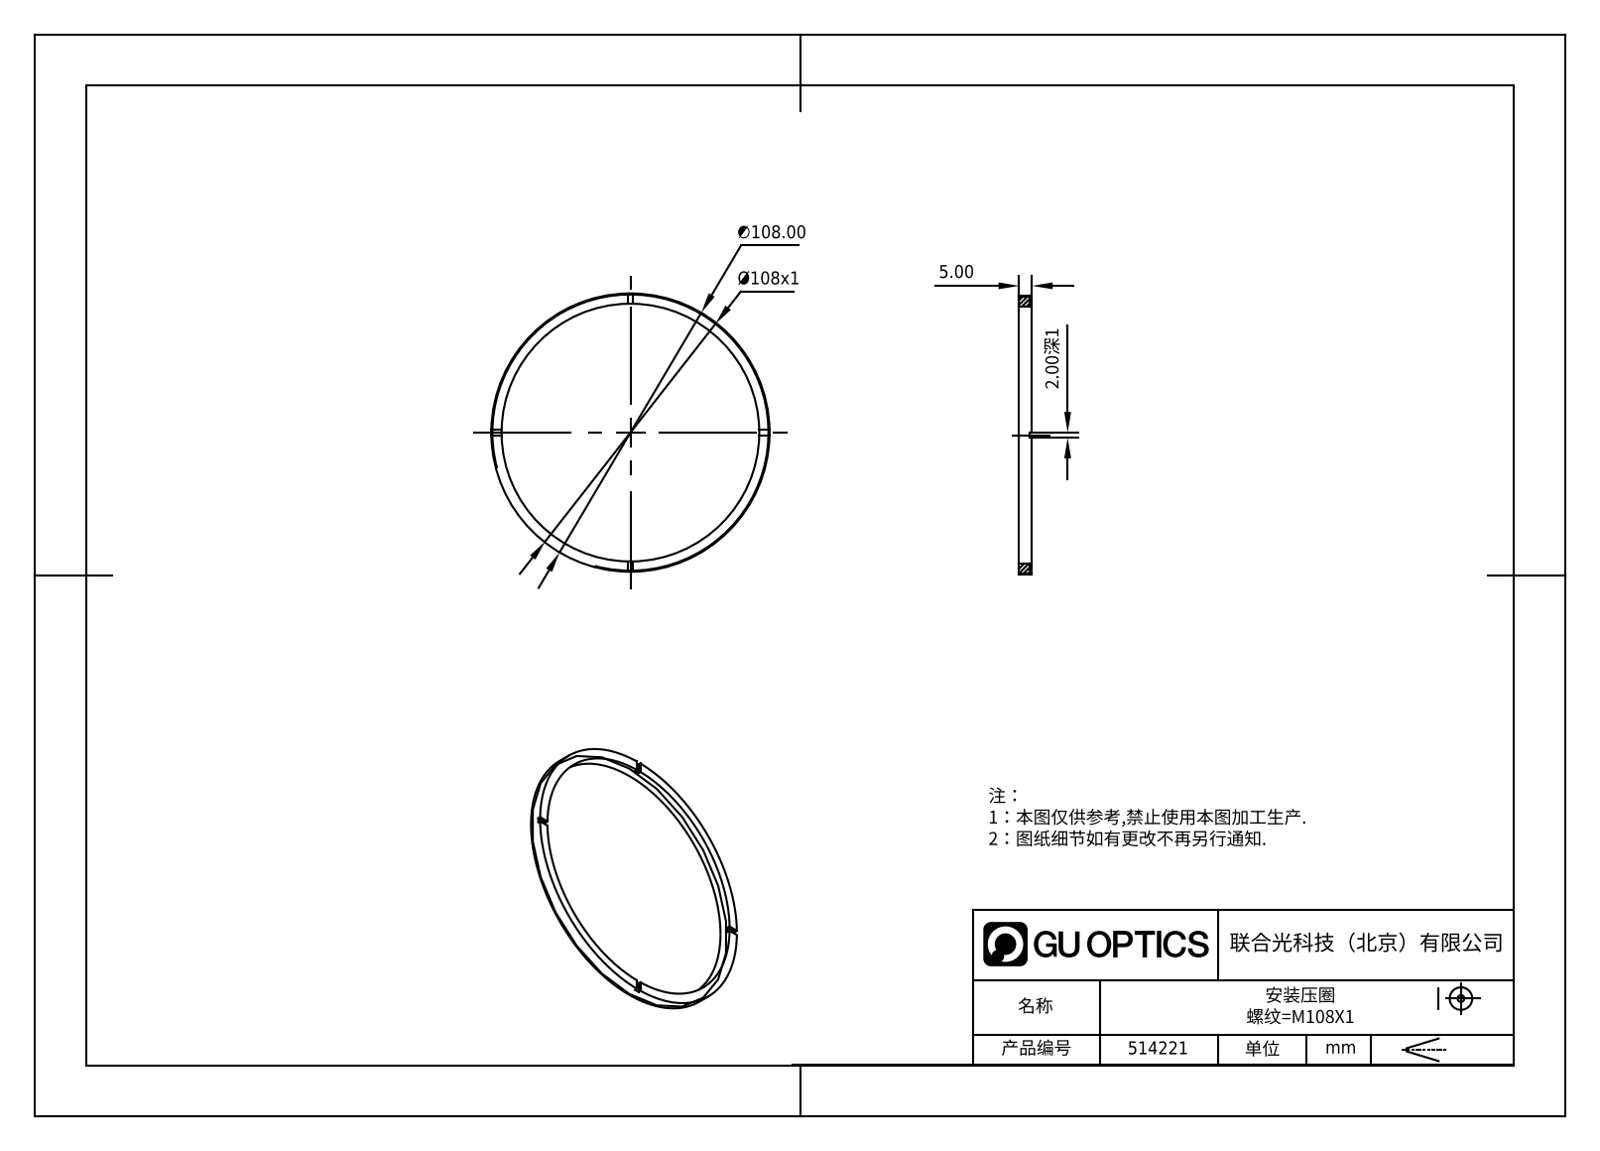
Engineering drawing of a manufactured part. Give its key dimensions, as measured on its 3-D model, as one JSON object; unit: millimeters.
{"part_name": "514221", "step_written_by": "SolidWorks 2020 (CONFIG_CONTROL_DESIGN)", "units": "millimeters", "bodies": {"solids": 1, "faces": 21, "planar": 17, "cylindrical": 4, "other": 0}, "overall_size": [108, 108, 5], "volume_mm3": 6503, "surface_area_mm2": 5897, "round_holes": [[100, 1]], "round_bosses_or_shafts": [[108, 1]], "face_to_face_distances": [5, 4, 1, 2]}
